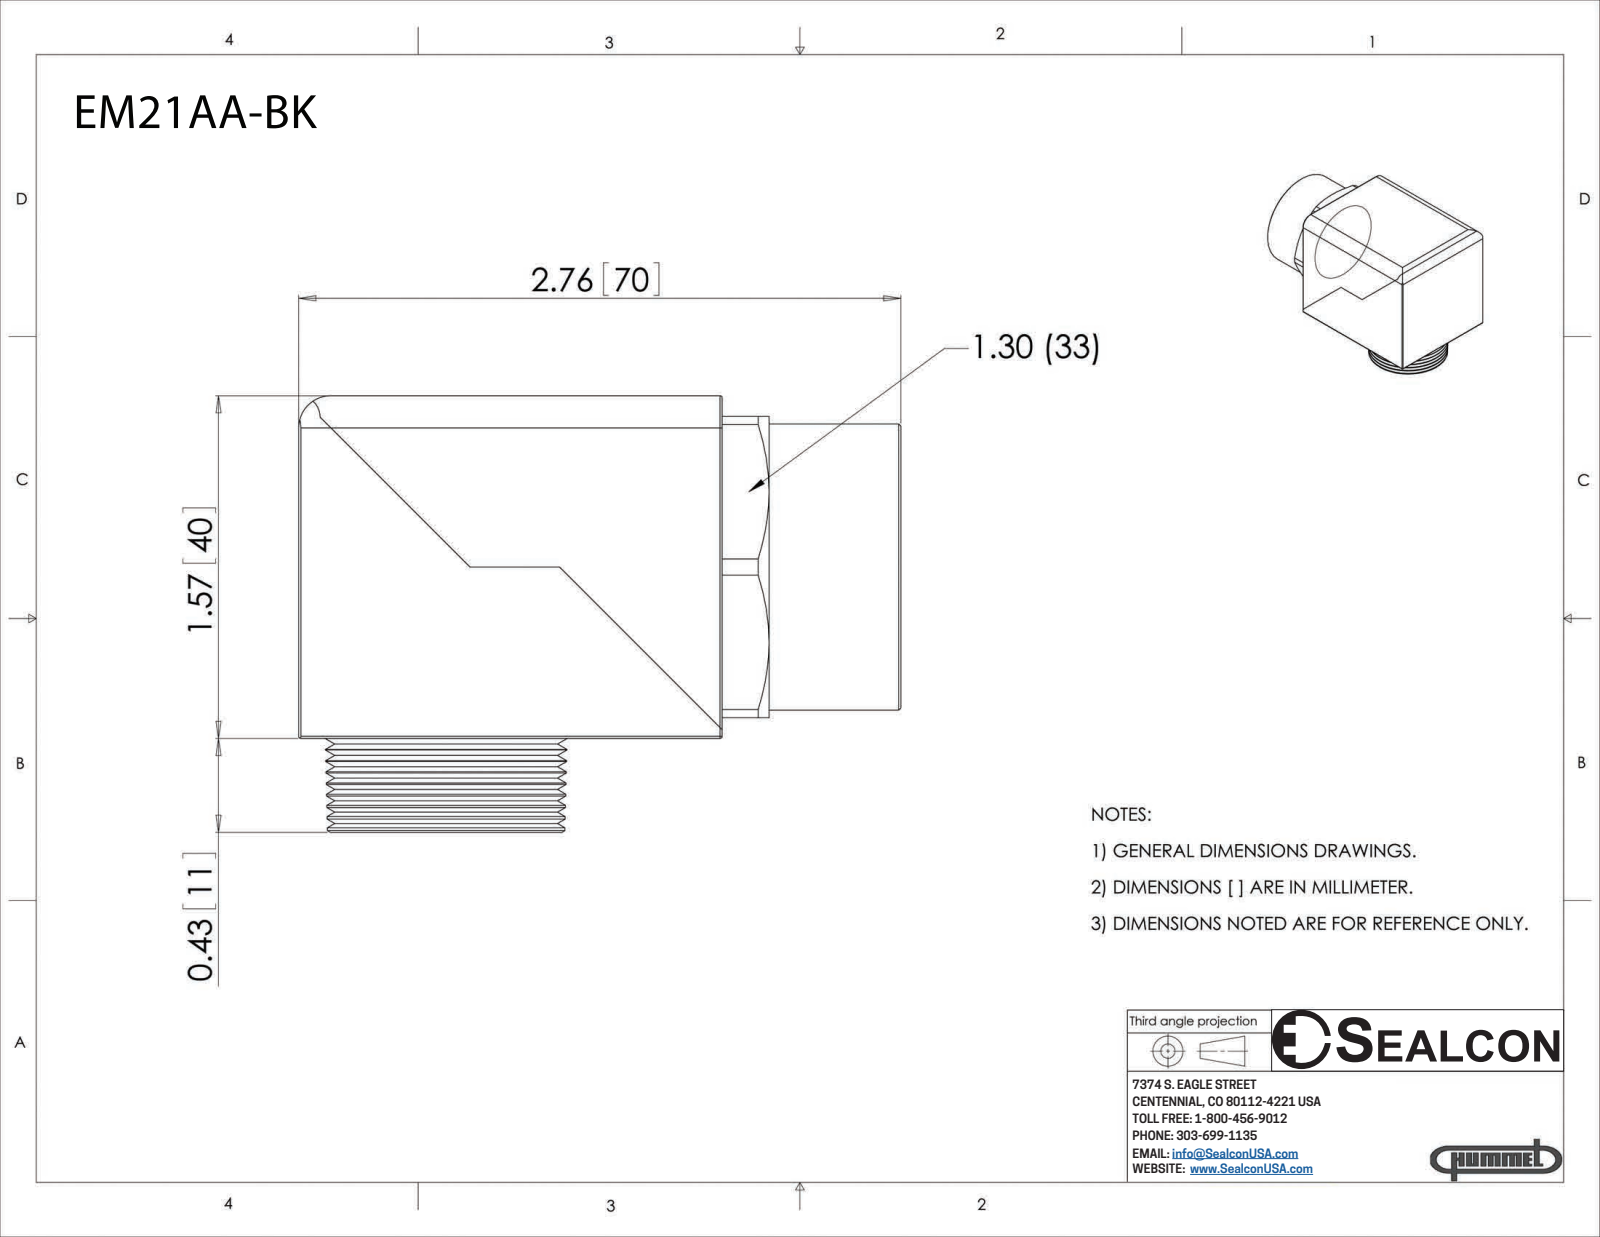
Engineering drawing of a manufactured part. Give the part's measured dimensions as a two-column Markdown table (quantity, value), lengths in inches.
| quantity | value |
| --- | --- |
| part name | EM21AA-BK |
| STEP written by | SolidWorks 2007 (AUTOMOTIVE_DESIGN) |
| units | inches |
| bodies | 2 solids, 134 faces (31 planar, 34 cylindrical, 69 other) |
| overall size | 2.75 × 2 × 1.57 |
| volume | 4.891 in³ |
| surface area | 37.24 in² |
| round holes (diameter × count) | 0.61 × 2, 1.12 × 1 |
| round bosses / shafts (diameter × count) | 1.311 × 1 |
| partial cylindrical surfaces (radius × count) | 0.01 × 7, 0.147 × 3, 0.098 × 1, 0.776 × 1 |
| main face-to-face distances | 1.57, 0.283, 1.931, 0.785, 0.215, 2.146, 0.43, 1.215, 2, 1.38 |
